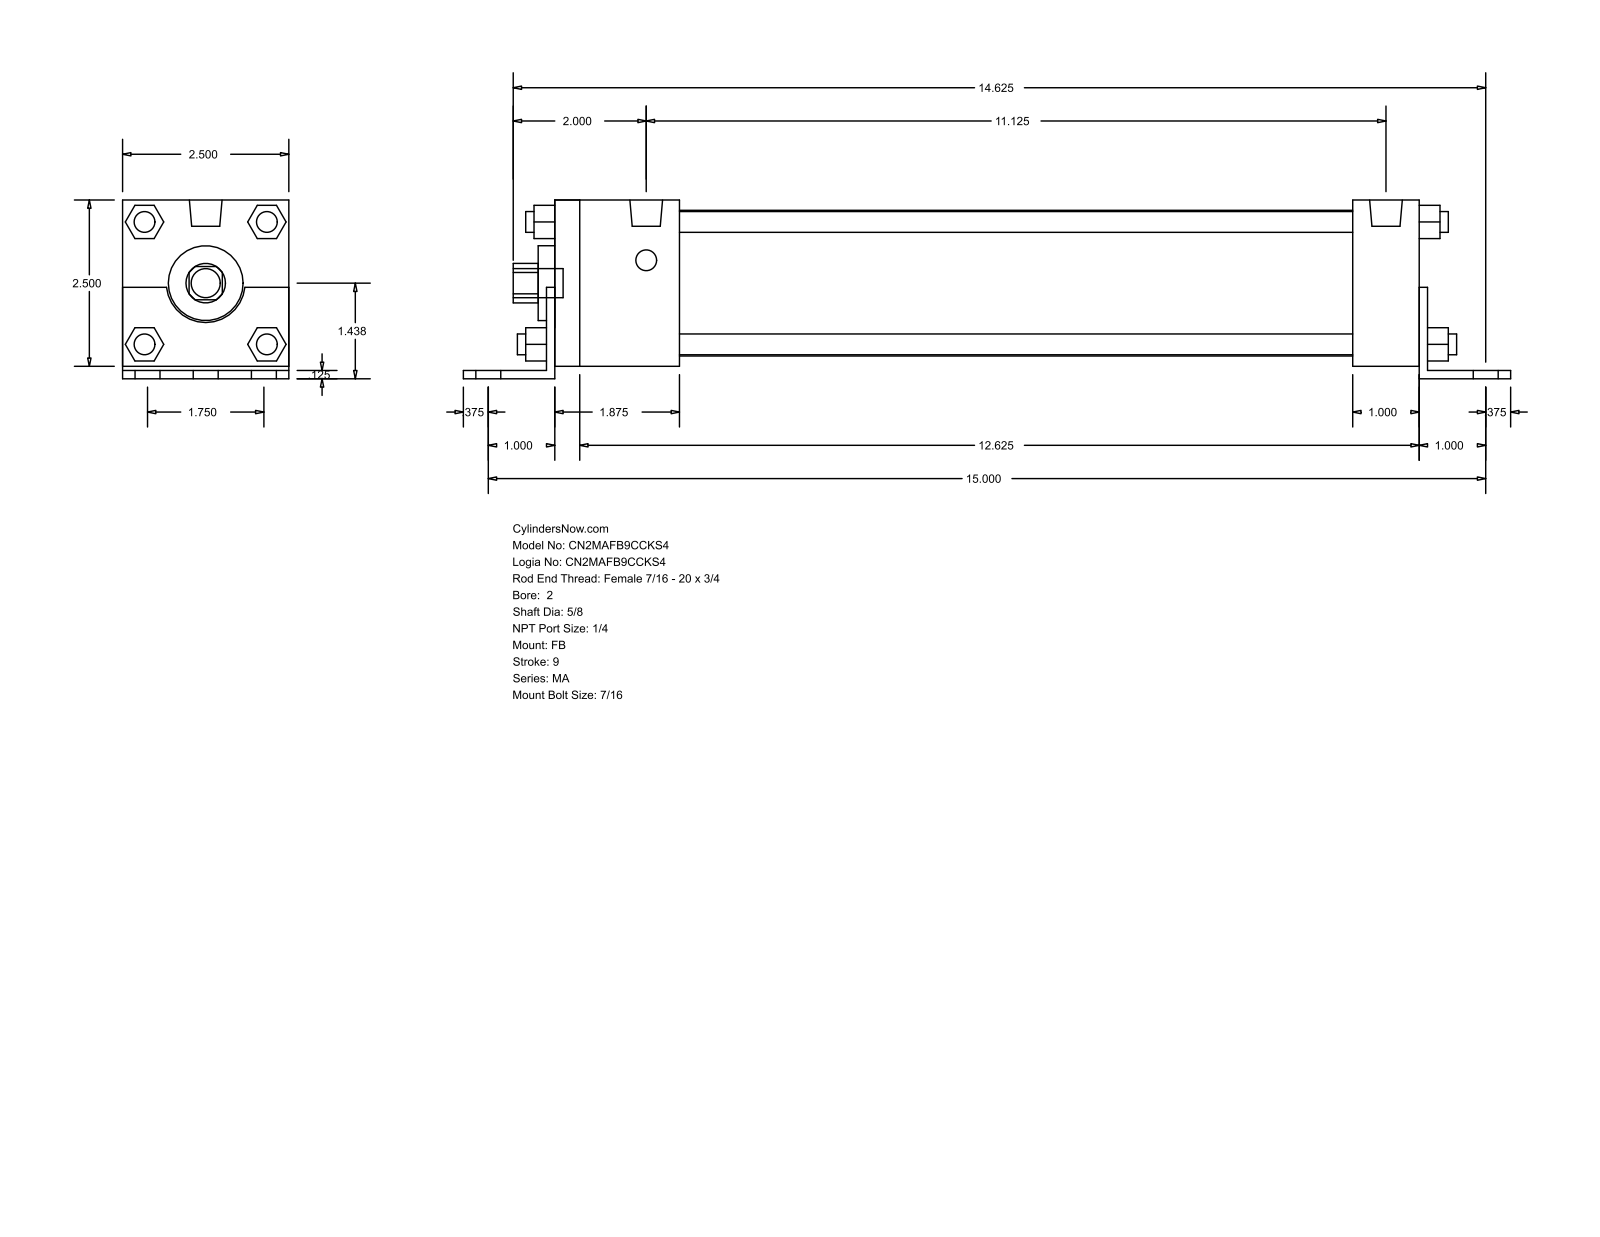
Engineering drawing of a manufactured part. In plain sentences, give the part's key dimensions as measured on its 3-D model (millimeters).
The part is named "MA_FB__0200_0.625". Its 3-D file was written by "GSSL Pune (CONFIG_CONTROL_DESIGN)". It is 0 solids with 140 faces: 105 planar, 35 cylindrical and 0 other. Overall it measures 400.05 by 68.26 by 63.5 millimeters. Round holes: 1 of diameter 15.88, 1 of diameter 28.57, 1 of diameter 55.63. Round bosses or shafts: 8 of diameter 7.94, 7 of diameter 11.11, 2 of diameter 12.49. Partial cylindrical surfaces (rounded edges, fillets, slot ends): 1 of radius 7.54, 1 of radius 15.05. The main face-to-face distances are 63.5, 4.76, 3.17, 68.26, 1.59, 3.18, 65.09, 333.37, 330.19, 12.7.
